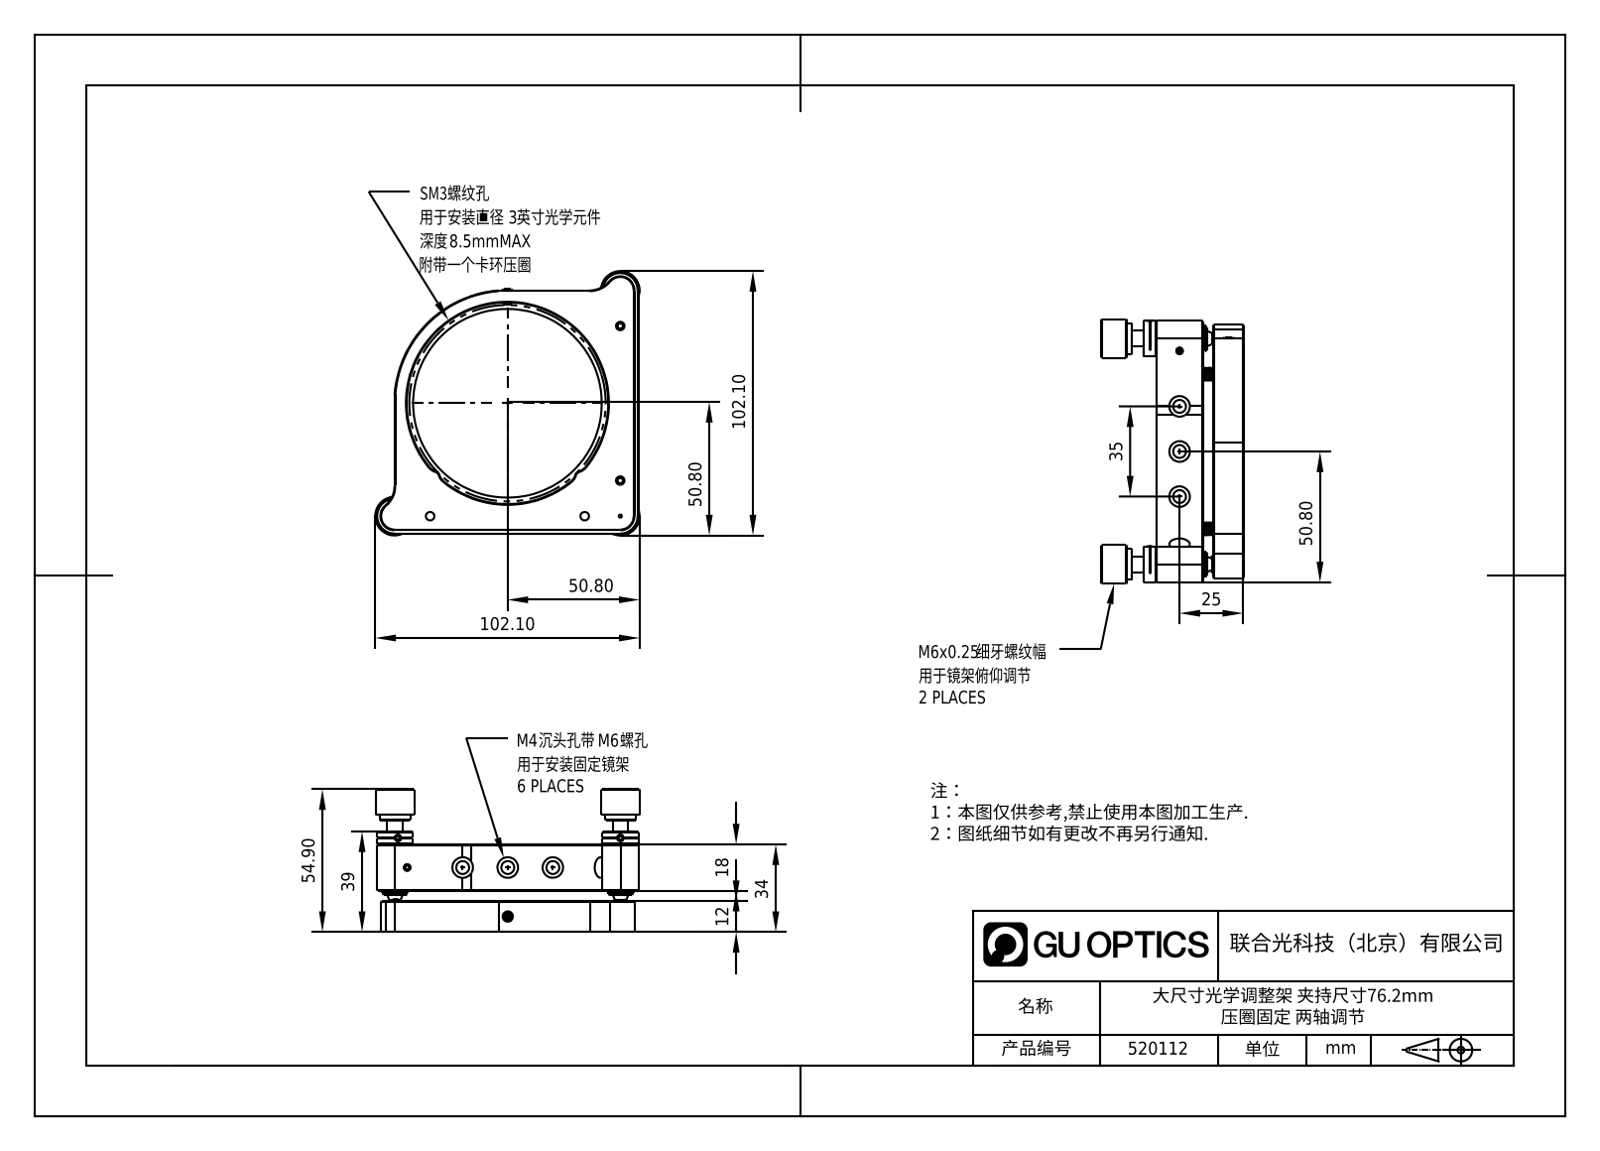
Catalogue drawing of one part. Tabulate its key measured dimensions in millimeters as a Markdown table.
| quantity | value |
| --- | --- |
| part name | 520112 |
| STEP written by | SolidWorks 2020 (CONFIG_CONTROL_DESIGN) |
| units | millimeters |
| bodies | 0 solids, 288 faces (138 planar, 81 cylindrical, 69 other) |
| overall size | 102.6 × 102.6 × 55.93 |
| round holes (diameter × count) | 5 × 6, 8 × 6, 6.5 × 4, 9.5 × 3, 1.2 × 1, 10 × 1, 71.4 × 1 |
| round bosses / shafts (diameter × count) | 3.3 × 4, 4 × 3, 15 × 2, 14 × 2, 8 × 2, 6 × 2, 3 × 2, 2 × 2 |
| partial cylindrical surfaces (radius × count) | 1.05 × 8, 10 × 4, 5.5 × 3, 0.2 × 2, 5 × 2, 7 × 1, 40 × 1, 43.94 × 1 |
| main face-to-face distances | 12, 22, 34, 16, 18, 4, 1.5, 13.5, 1, 11 |
| hole center spacings | 13.8, 17.5, 53.09, 73.8, 61.94, 35, 60, 75.08 |
